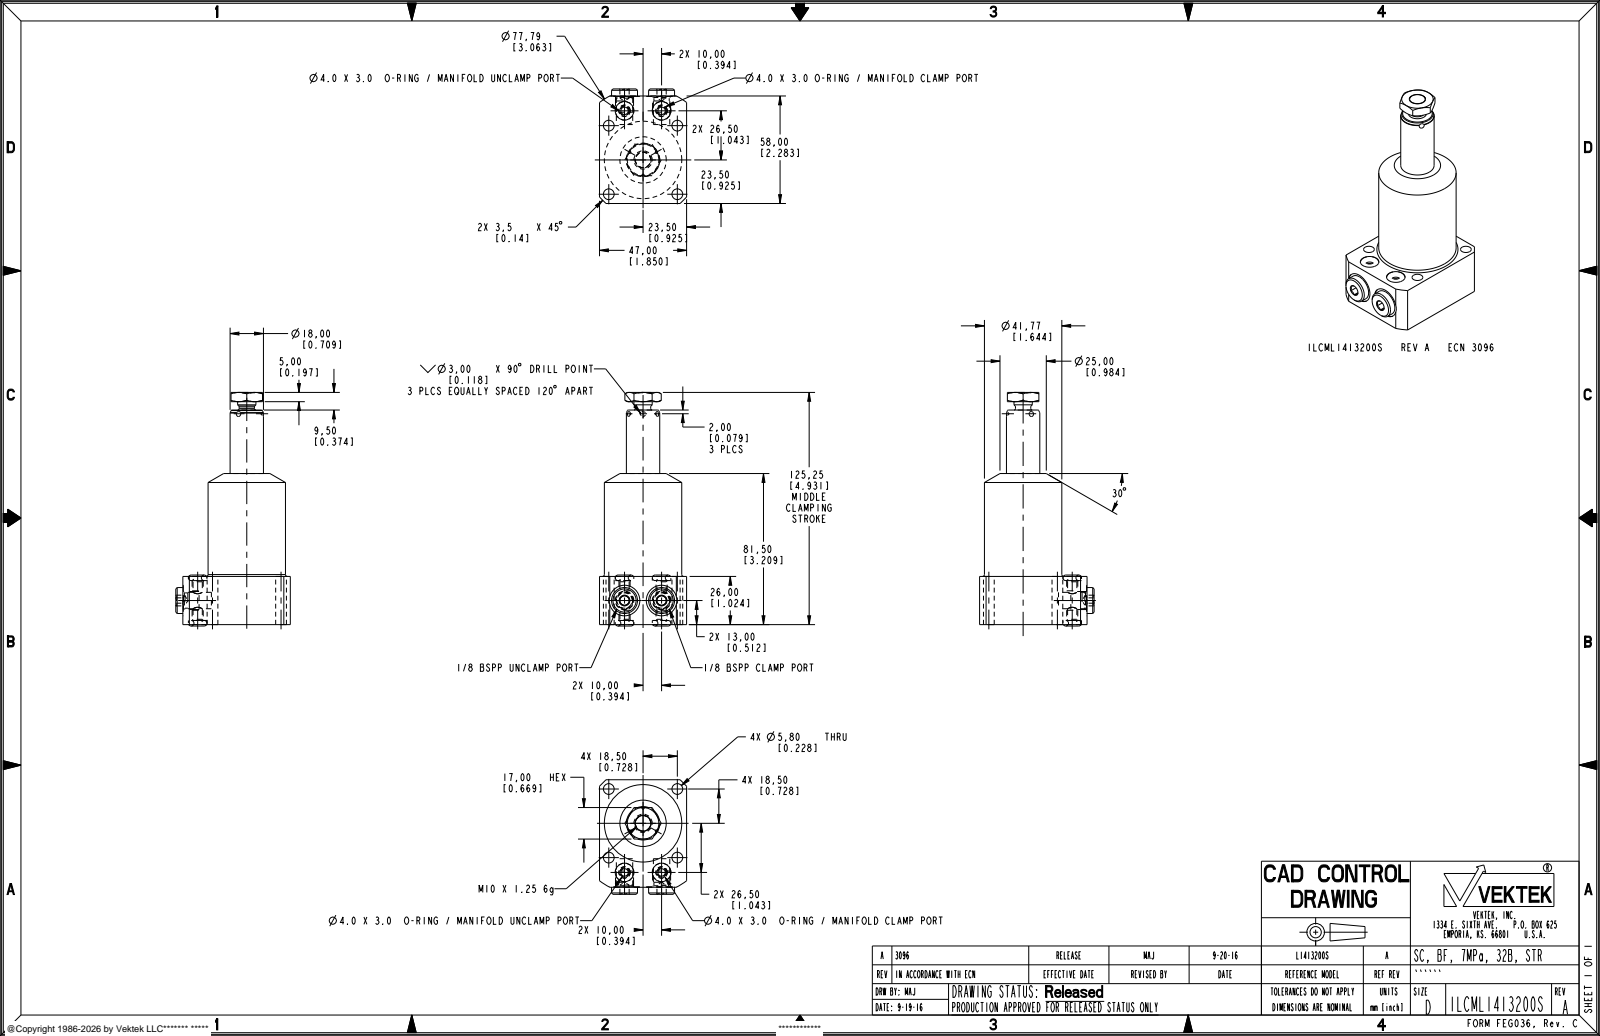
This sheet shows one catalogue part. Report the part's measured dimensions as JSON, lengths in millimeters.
{"part_name": "ILCML1413200S", "step_written_by": "PRO/ENGINEER BY PARAMETRIC TECHNOLOGY CORPORATION, 2013320 (AUTOMOTIVE_DESIGN)", "units": "millimeters", "bodies": {"solids": 5, "faces": 204, "planar": 63, "cylindrical": 64, "other": 77}, "overall_size": [126, 61.81, 47], "volume_mm3": 149981, "surface_area_mm2": 25838, "round_holes": [[5.8, 4], [5, 2], [8.84, 2], [10, 2], [16.5, 2], [8.75, 1]], "round_bosses_or_shafts": [[8.25, 3], [14, 2], [9.73, 2], [6, 2], [41.77, 1], [18, 1], [9.87, 1]], "partial_cylinders_radius": [[38.9, 1]], "face_to_face_distances": [47, 26, 58, 57.75, 5, 81.5, 55.5, 125.25, 99.25, 43.75], "hole_center_spacings": [26.16, 37, 11.67, 20, 28.32, 29.6, 45.8, 52.33]}
